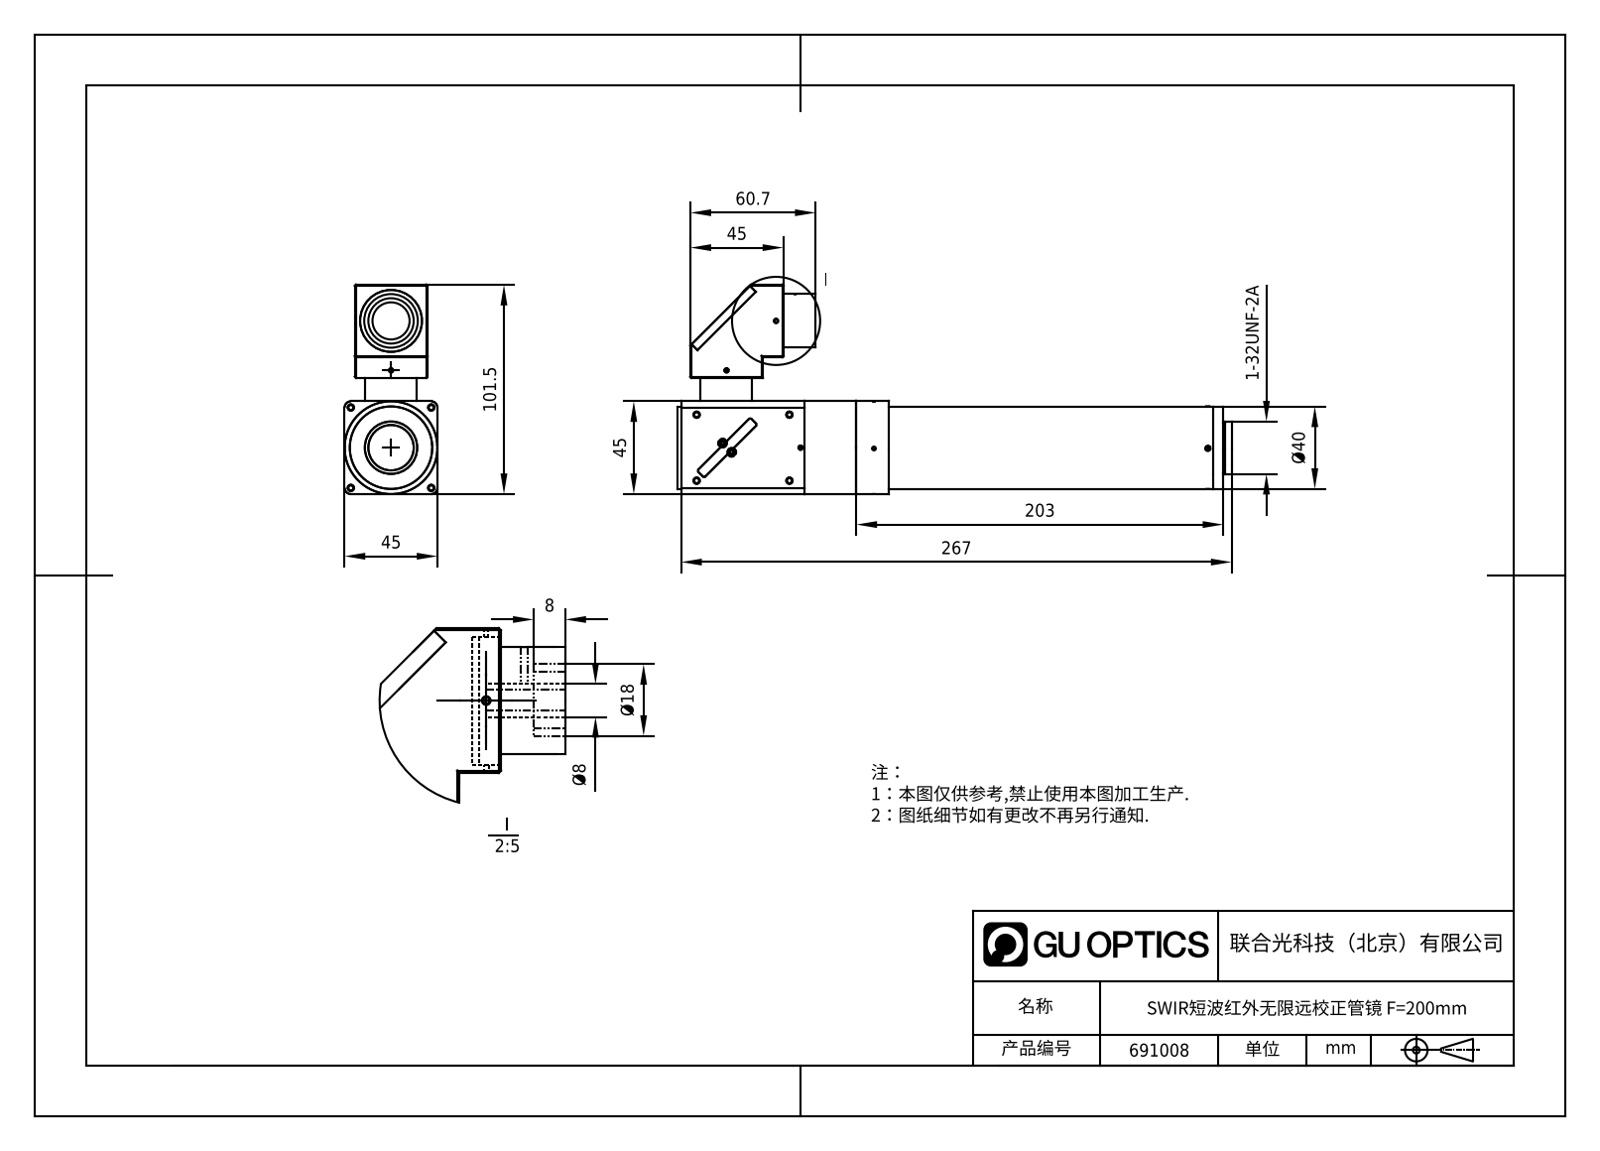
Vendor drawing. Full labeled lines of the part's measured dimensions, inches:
Part name (STEP PRODUCT): 691008
STEP written by: SolidWorks 2020 (CONFIG_CONTROL_DESIGN)
Units: inches
Bodies: 17 solids, 396 faces (173 planar, 140 cylindrical, 83 other)
Overall size (bounding box): 10.591 × 3.996 × 1.772
Volume: 11.67 in³ · Surface area: 189.7 in²
Round holes (diameter × count): ⌀0.098 ×20, ⌀0.063 ×17, ⌀0.079 ×4, ⌀0.866 ×3, ⌀0.039 ×2, ⌀0.087 ×2, ⌀0.709 ×2, ⌀1.181 ×2, ⌀0.315 ×1, ⌀0.551 ×1, ⌀0.63 ×1, ⌀0.787 ×1
Round bosses / shafts (diameter × count): ⌀1.772 ×1, ⌀1.575 ×1, ⌀1.417 ×1, ⌀1.339 ×1, ⌀1.299 ×1, ⌀1.024 ×1, ⌀1 ×1, ⌀0.984 ×1
Partial cylindrical surfaces — rounded edges, fillets, slot ends (radius × count): R0.039 ×8, R0.02 ×4, R0.059 ×4, R0.118 ×4
Main face-to-face distances: 1.772, 0.197, 0.157, 1.575, 1.378, 0.079, 0.236, 1.791, 2.323, 1.634
Hole centre spacings: 6.378, 1.086, 1.26, 0.176, 0.948, 1.102, 1.192, 1.513
